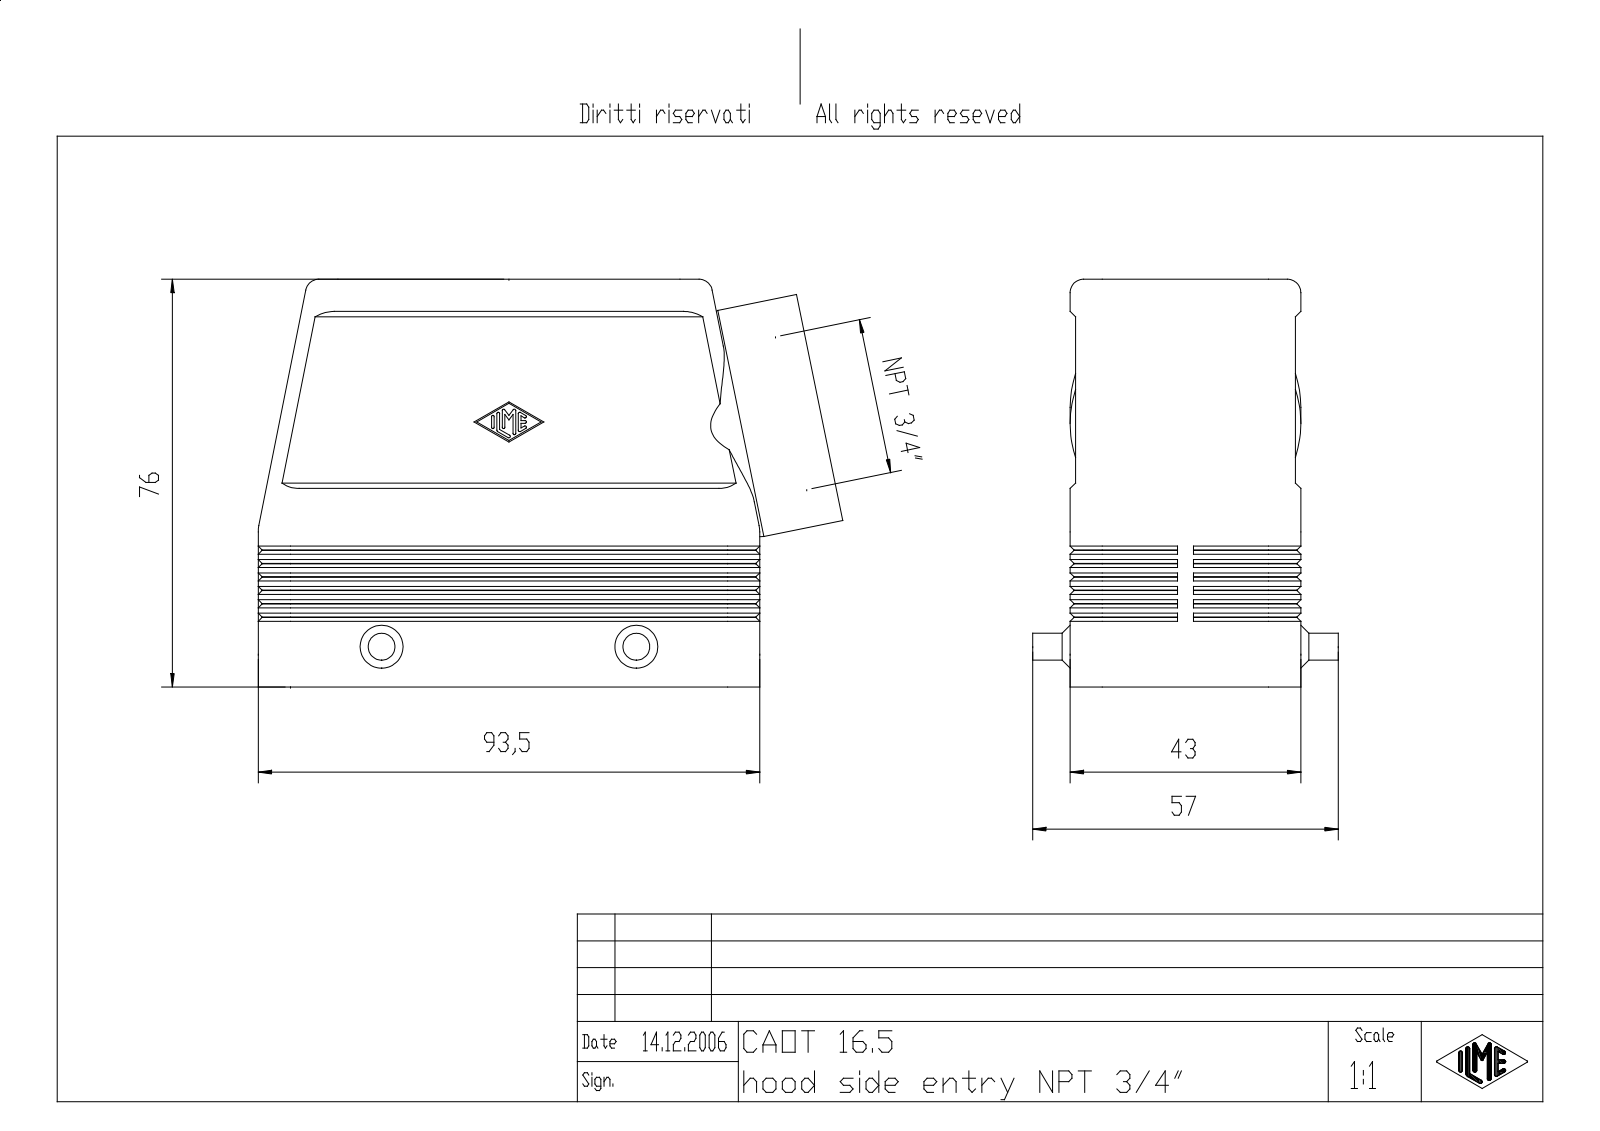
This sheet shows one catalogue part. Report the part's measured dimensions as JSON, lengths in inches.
{"part_name": "MSBO8705", "step_written_by": "Creo Elements/Direct Modeling 18.0B 02-Dec-2011 (C) Parametric Technology GmbH (AUTOMOTIVE_DESIGN)", "units": "inches", "bodies": {"solids": 1, "faces": 428, "planar": 230, "cylindrical": 122, "other": 76}, "overall_size": [4.291, 2.992, 2.244], "volume_in3": 4.981, "surface_area_in2": 72.19, "round_holes": [[0.157, 4], [0.097, 3], [0.097, 1], [1.054, 1]], "round_bosses_or_shafts": [[0.197, 2], [1.693, 1]], "partial_cylinders_radius": [[0.01, 14], [0.236, 12], [0.079, 4], [0.098, 4], [0.118, 4], [0.209, 4]], "face_to_face_distances": [0.118, 1.457, 0.079, 1.535, 0.039, 1.654, 1.575, 1.614, 1.693, 0.07], "hole_center_spacings": [1.063, 3.051, 3.231]}
